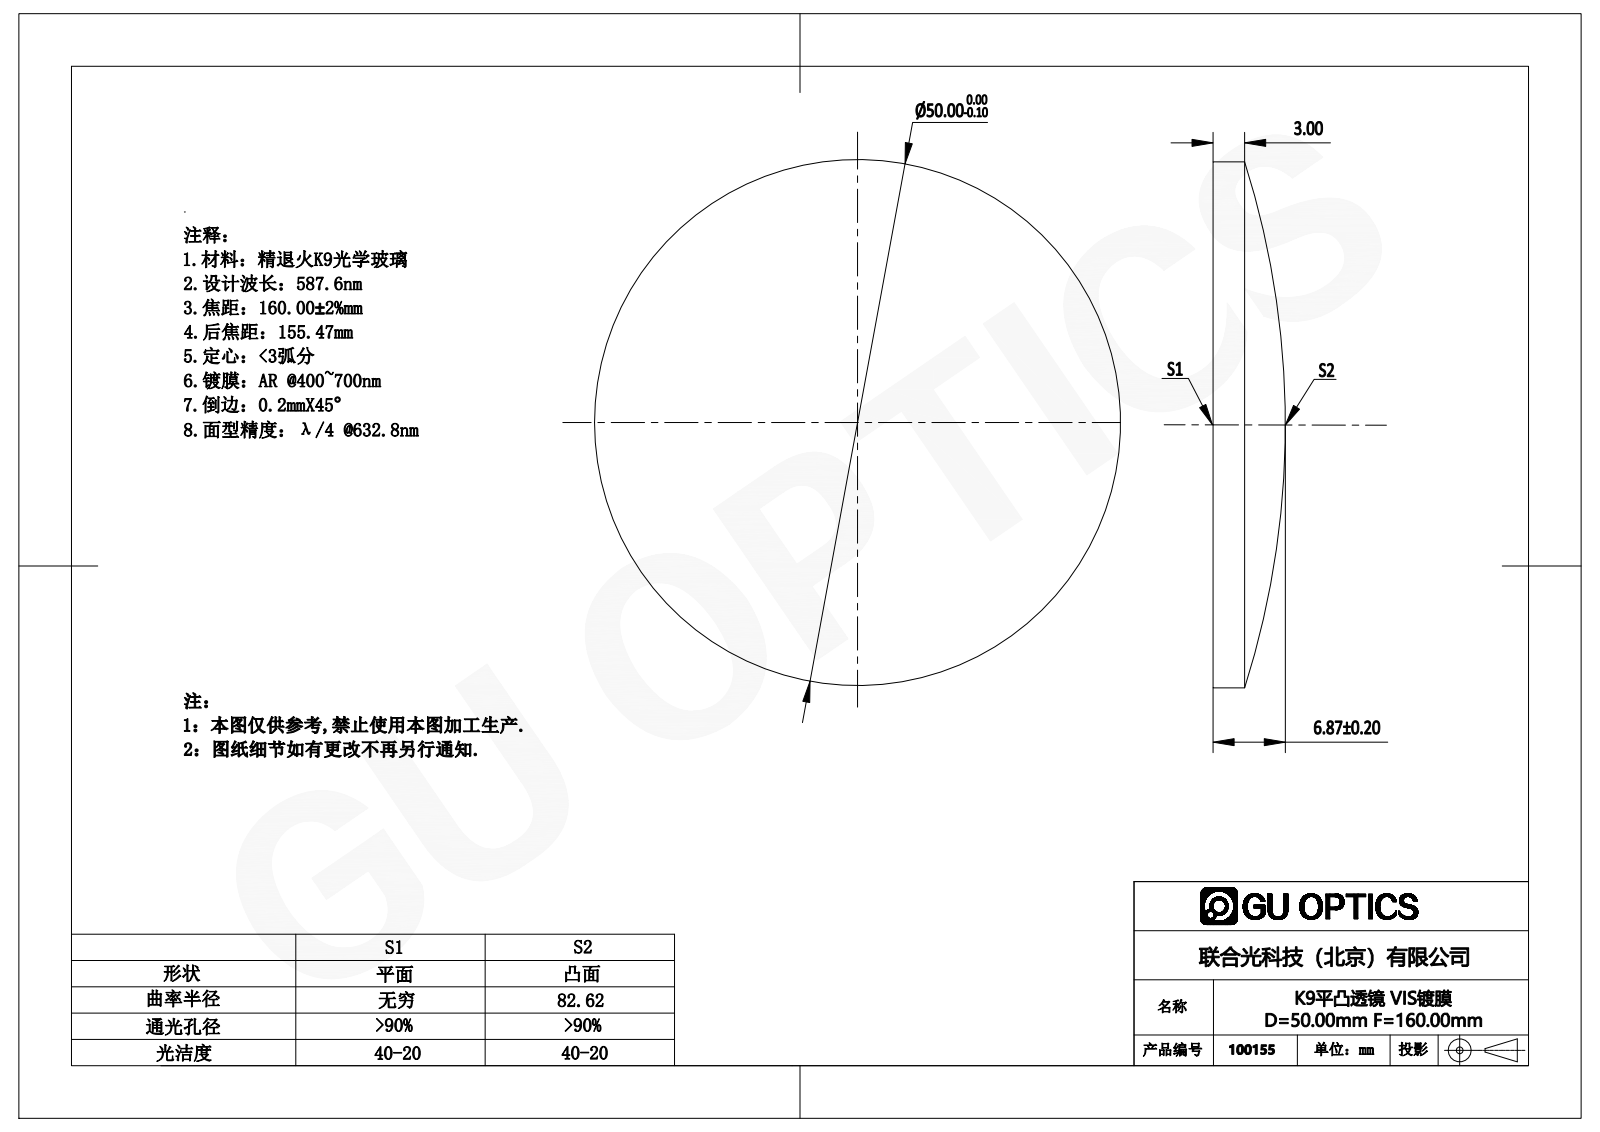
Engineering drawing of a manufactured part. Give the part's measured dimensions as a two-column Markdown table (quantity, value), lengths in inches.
| quantity | value |
| --- | --- |
| part name | 100155 |
| STEP written by | SolidWorks 2016 (AUTOMOTIVE_DESIGN) |
| units | inches |
| bodies | 1 solid, 6 faces (0 planar, 0 cylindrical, 6 other) |
| overall size | 1.969 × 1.969 × 0.274 |
| volume | 0.593 in³ |
| surface area | 6.893 in² |
